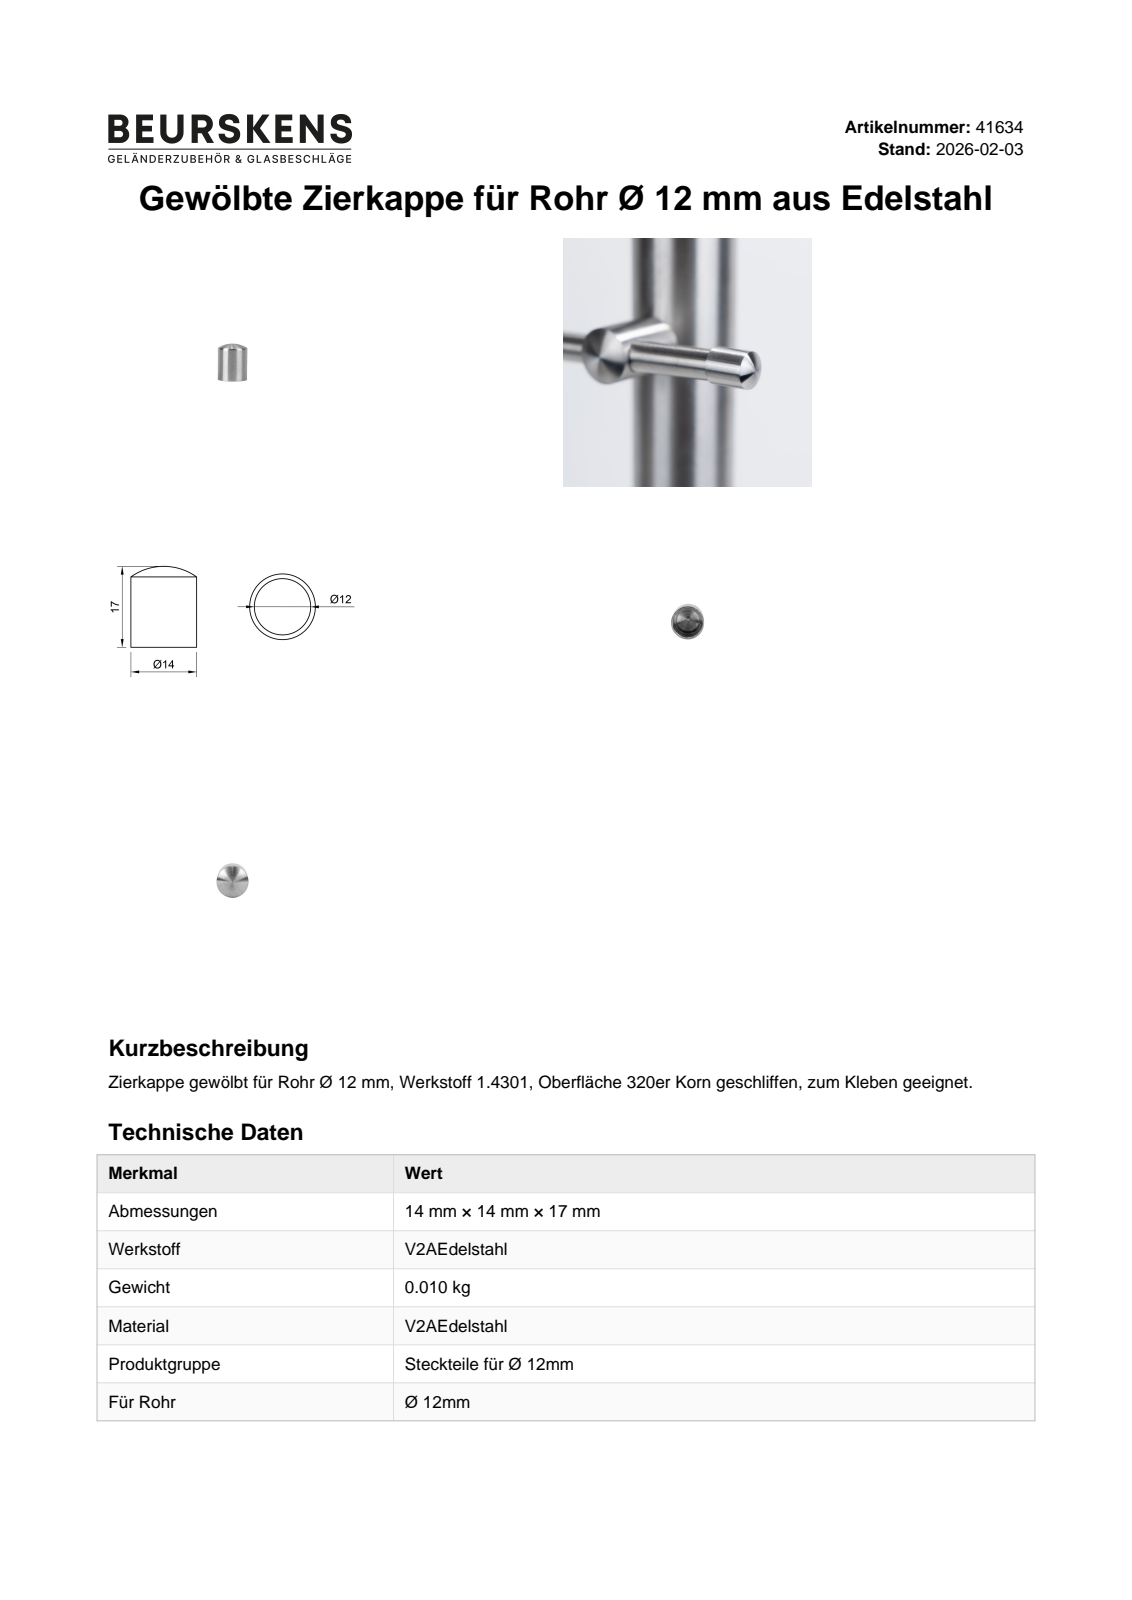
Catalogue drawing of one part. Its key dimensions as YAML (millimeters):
part_name: "41634"
step_written_by: "Autodesk Inventor 2022 (AUTOMOTIVE_DESIGN)"
units: millimeters
bodies: {solids: 1, faces: 5, planar: 1, cylindrical: 2, other: 2}
overall_size: [17.25, 14, 14]
volume: 1222
surface_area: 1379
round_holes:
  - {diameter: 12, count: 1}
round_bosses_or_shafts:
  - {diameter: 14, count: 1}
